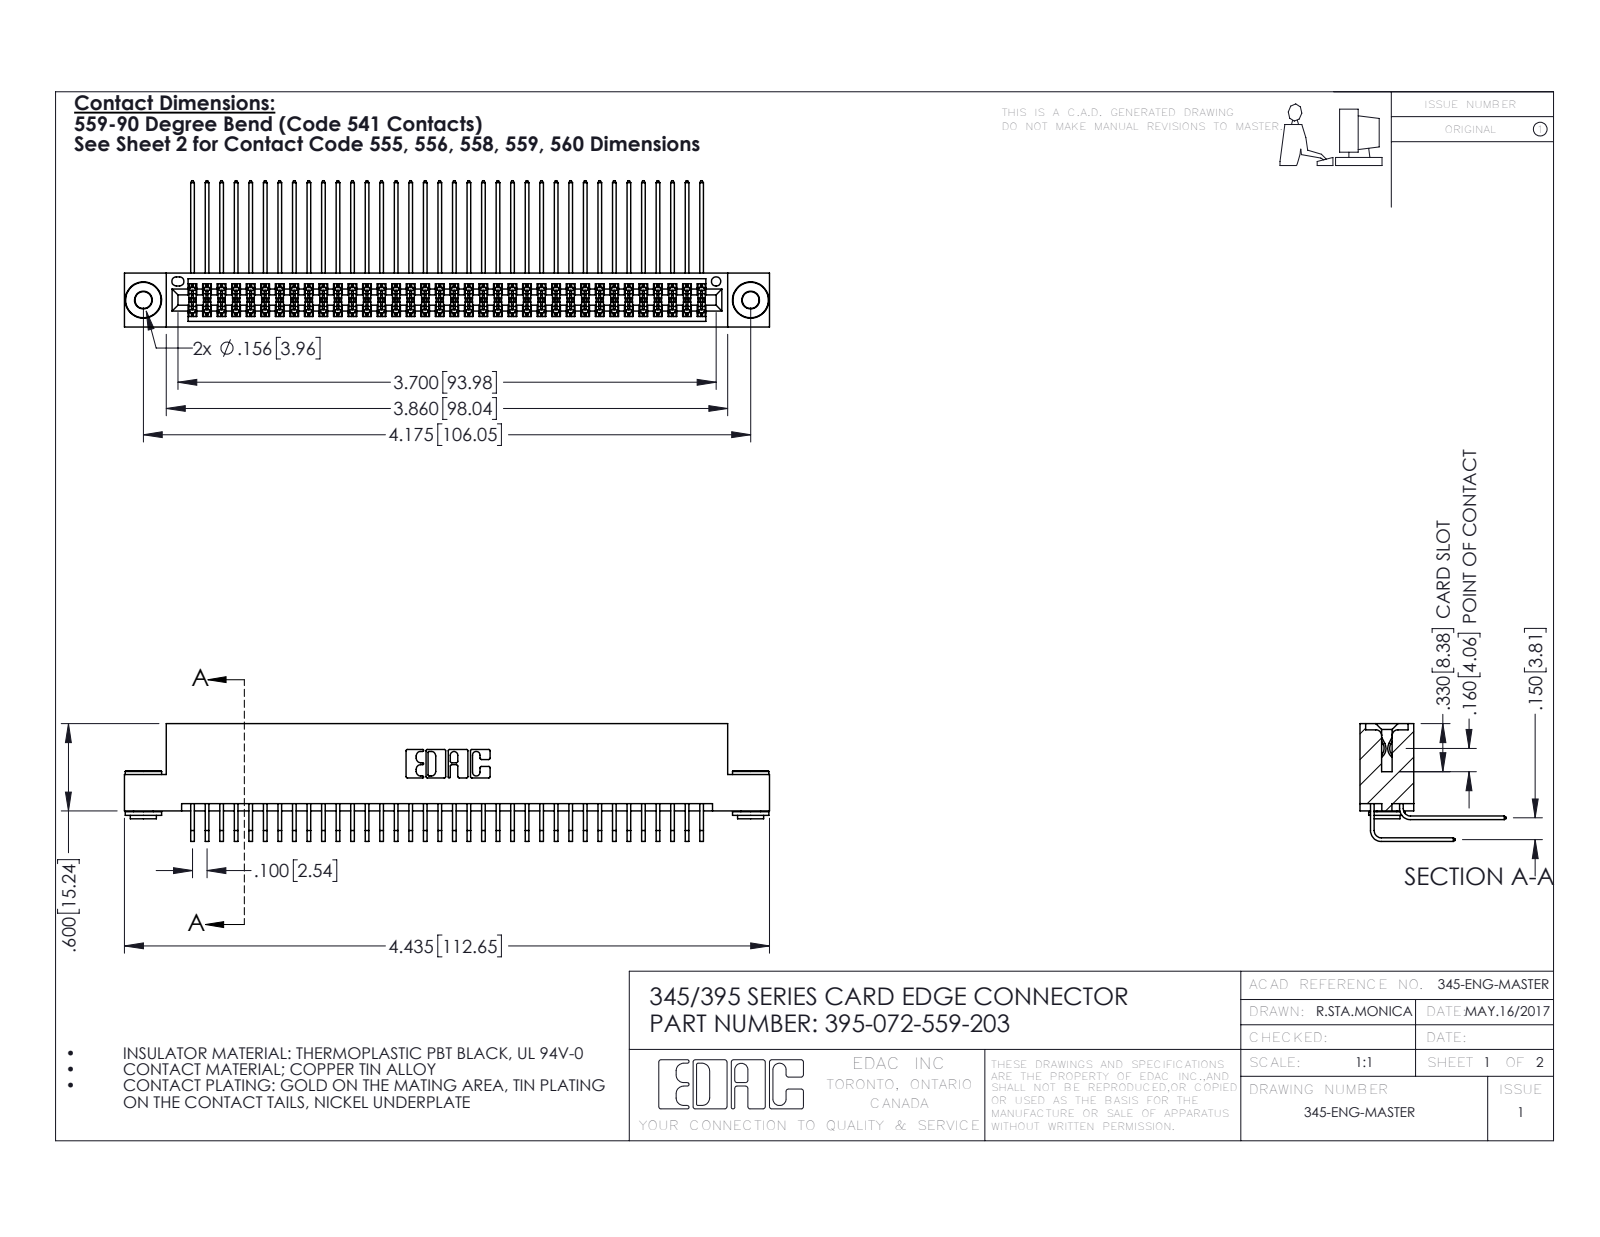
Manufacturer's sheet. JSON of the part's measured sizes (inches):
{"part_name": "345-292-001_558 559 Tail - 1; 345 Part_Flush Mounting Lugs - 0.156 Dia-TH; 395-072-559-203; 345-250-002_345-250-002-102 (+1 more)", "step_written_by": "SolidWorks 2016 (CONFIG_CONTROL_DESIGN)", "units": "inches", "bodies": {"solids": 75, "faces": 3908, "planar": 2610, "cylindrical": 1290, "other": 8}, "overall_size": [4.435, 1.005, 0.809], "volume_in3": 0.691, "surface_area_in2": 29.11, "round_holes": [[0.116, 2], [0.156, 2], [0.064, 1]], "round_bosses_or_shafts": [[0.25, 2], [0.18, 2], [0.136, 2]], "partial_cylinders_radius": [[0.006, 108], [0.01, 22], [0.007, 6], [0.031, 6], [0.026, 3], [0.014, 2], [0.019, 2], [0.022, 2]], "face_to_face_distances": [0.072, 0.298, 0.2, 0.37, 0.025, 0.098, 0.272, 0.225, 0.175, 0.15], "hole_center_spacings": [0.27, 3.939, 4.175]}
